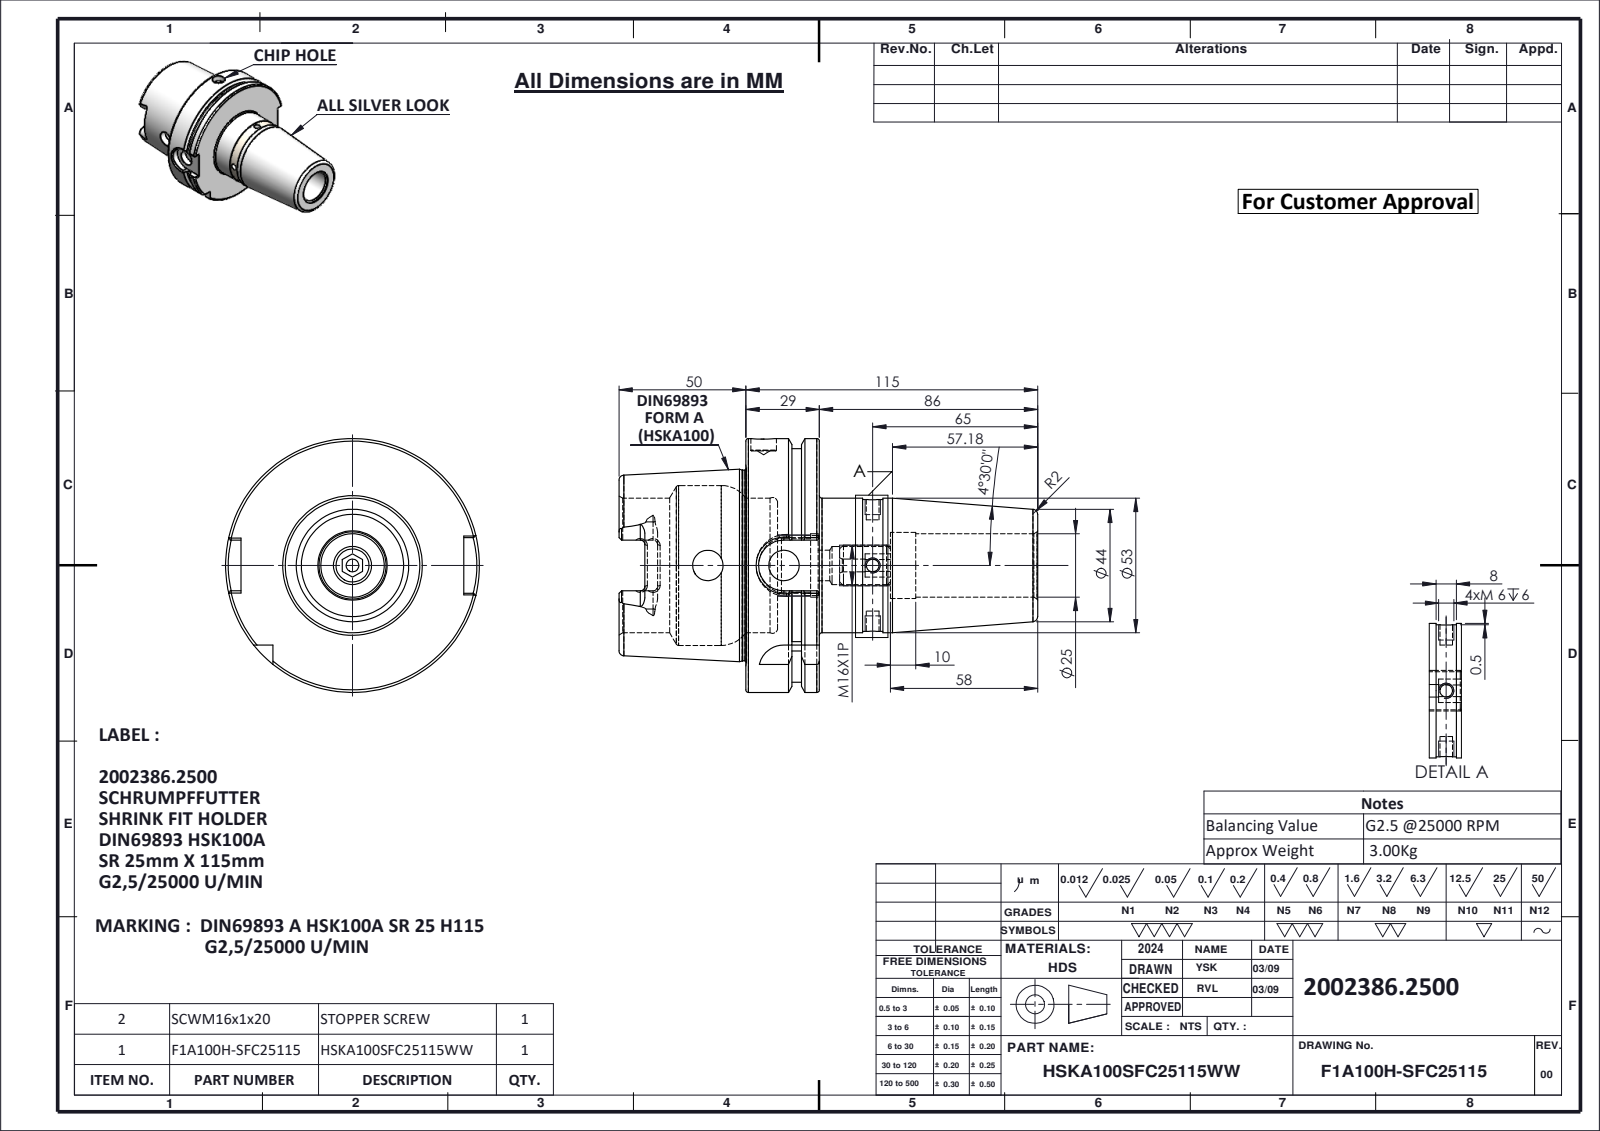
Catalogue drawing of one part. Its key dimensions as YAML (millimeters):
part_name: "F1A100H-SFC25115; SCWM16X1P; HSKA100SFC25115"
step_written_by: "SolidWorks 2024 (CONFIG_CONTROL_DESIGN)"
units: millimeters
bodies: {solids: 2, faces: 218, planar: 68, cylindrical: 70, other: 80}
overall_size: [164.95, 100, 100]
volume: 391362
surface_area: 70571
round_holes:
  - {diameter: 5, count: 3}
  - {diameter: 12, count: 3}
  - {diameter: 10, count: 1}
  - {diameter: 15, count: 1}
  - {diameter: 21, count: 1}
  - {diameter: 25, count: 1}
  - {diameter: 26, count: 1}
  - {diameter: 53, count: 1}
  - {diameter: 63, count: 1}
round_bosses_or_shafts:
  - {diameter: 100, count: 1}
  - {diameter: 92, count: 1}
  - {diameter: 75.16, count: 1}
  - {diameter: 52, count: 1}
  - {diameter: 16, count: 1}
partial_cylinders:
  - {radius: 1.8, count: 6}
  - {radius: 4.88, count: 4}
  - {radius: 10, count: 2}
  - {radius: 11, count: 1}
face_to_face_distances: [28.95, 12.5, 16.45, 50, 62.5, 78.95, 164.95, 114.95, 102.45, 86]
hole_center_spacings: [30, 34.95, 42.95, 64.95]
